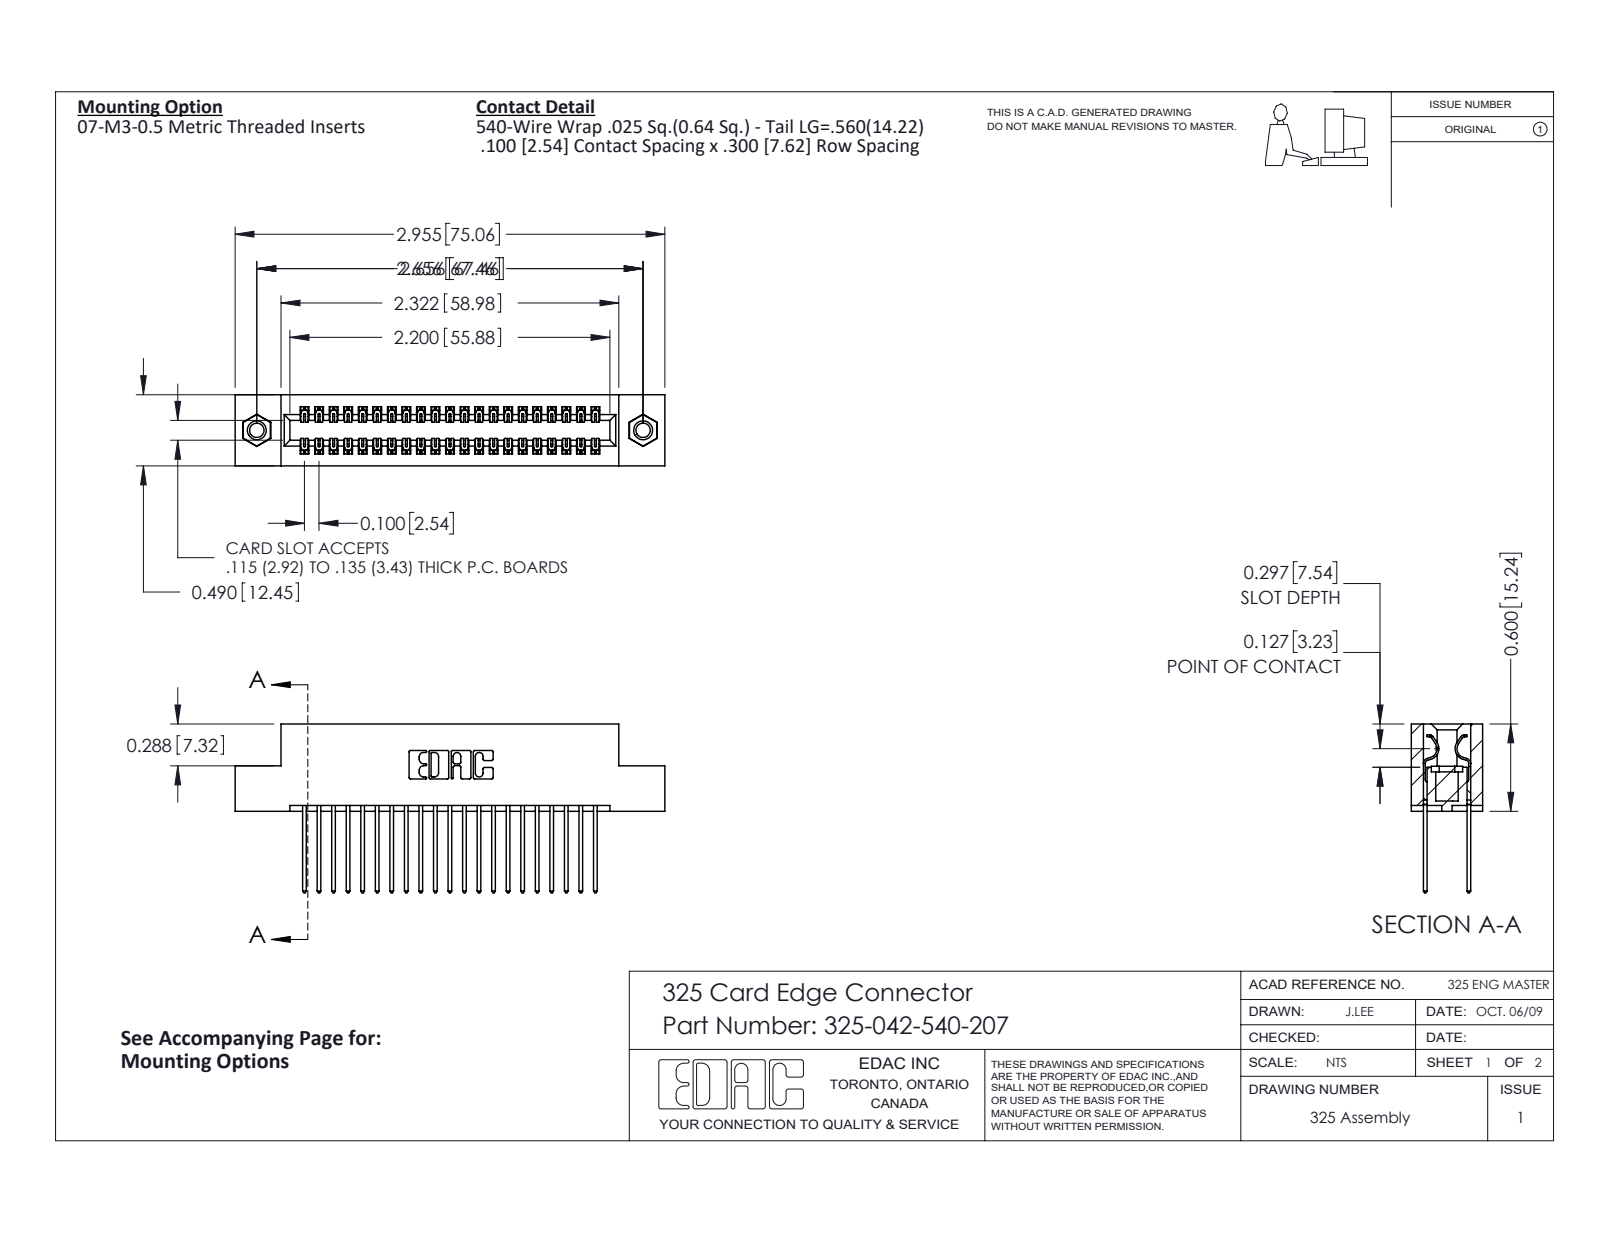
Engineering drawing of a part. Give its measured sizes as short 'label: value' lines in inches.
name: 345-250-001_345-250-005-103; 325-292-001_325-293-140; 325 Part_TI; 325-042-540-207
written by: SolidWorks 2016 (CONFIG_CONTROL_DESIGN)
unit: in
bodies: 45 solids, 2358 faces (1614 planar, 728 cylindrical, 16 other)
size: 2.955 × 1.16 × 0.49
volume: 0.589 in³; area: 18.54 in²
holes: 2× ⌀0.098, 2× ⌀0.125, 2× ⌀0.16
bosses: 2× ⌀0.155
rounds: 63× R0.006, 42× R0.01, 22× R0.01, 6× R0.007, 6× R0.031, 3× R0.026, 2× R0.014, 2× R0.022
face distances: 0.083, 0.407, 0.3, 0.107, 0.383, 0.025, 0.49, 0.325, 0.6, 0.04
hole spacings: 2.656
